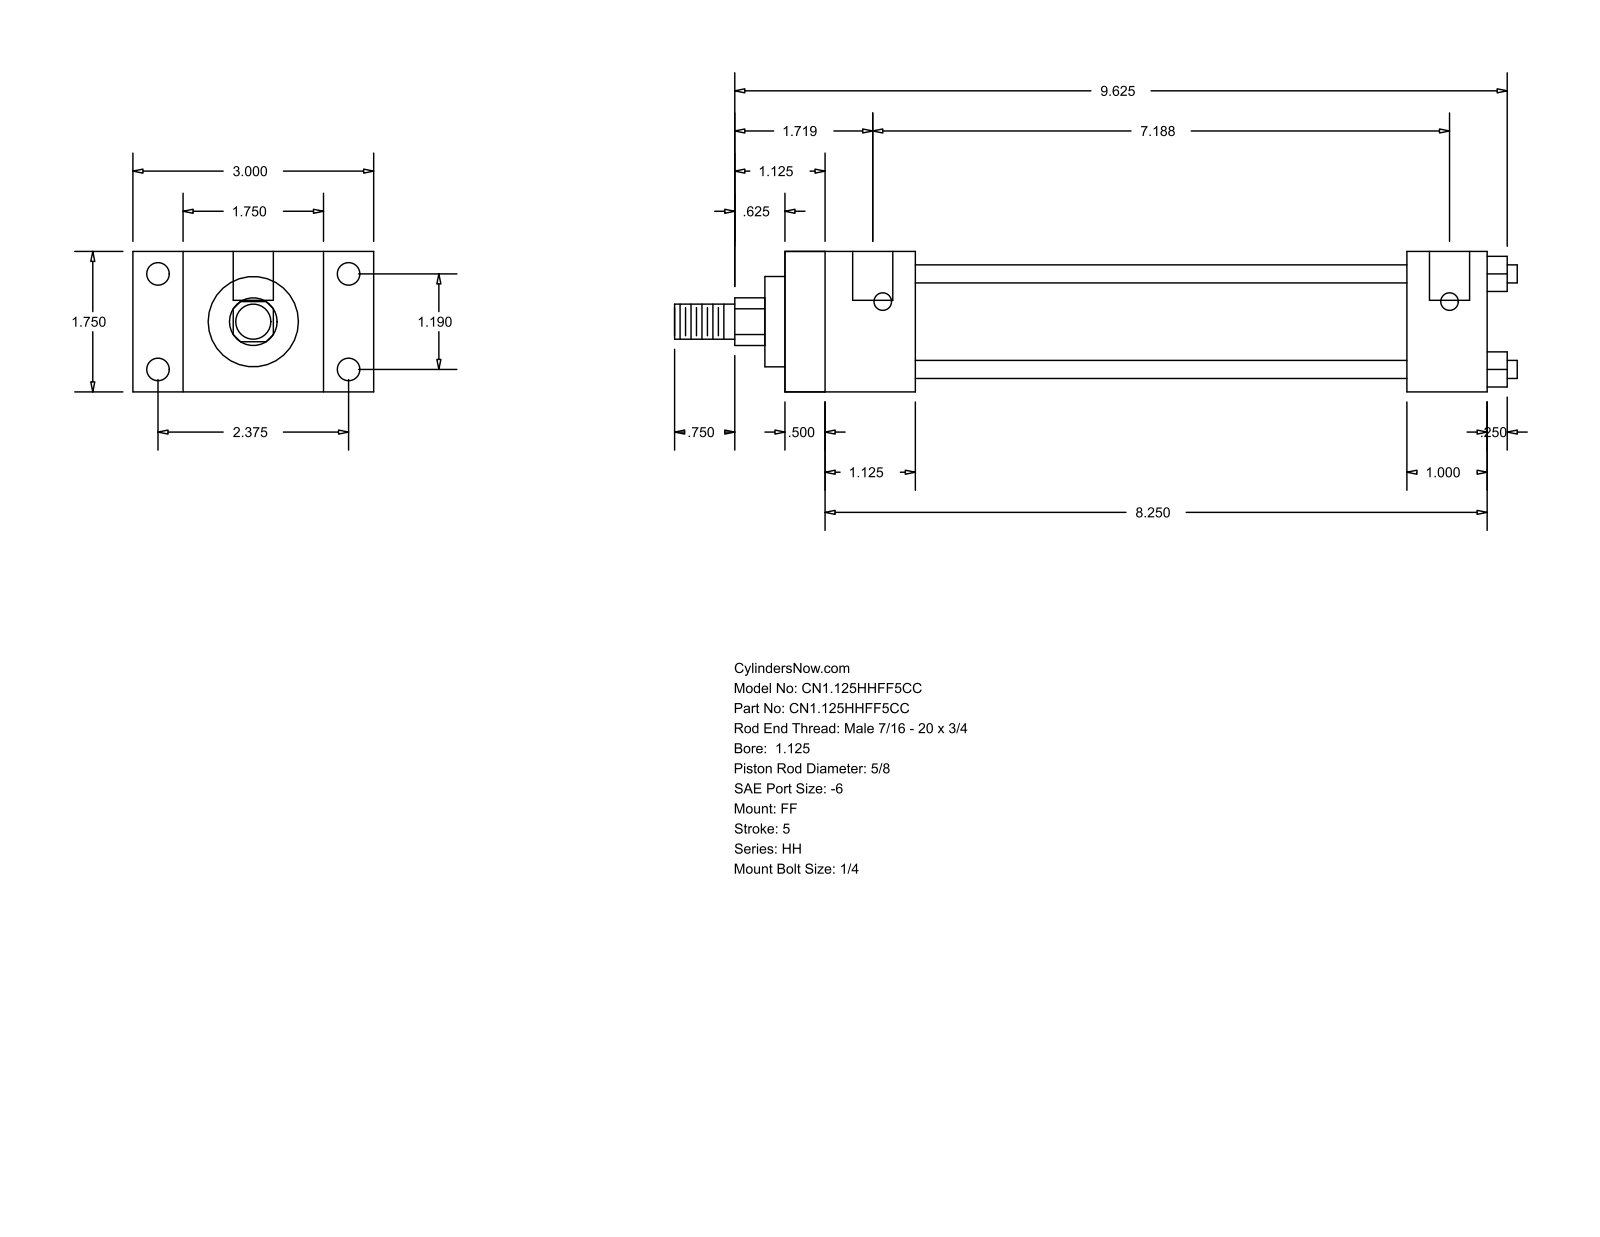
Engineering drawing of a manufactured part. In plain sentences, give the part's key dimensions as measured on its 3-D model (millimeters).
The part is named "HH_FF__0112_0.625". Its 3-D file was written by "GSSL Pune (CONFIG_CONTROL_DESIGN)". It is 0 solids with 92 faces: 64 planar, 28 cylindrical and 0 other. Overall it measures 266.7 by 76.2 by 44.45 millimeters. Round holes: 4 of diameter 5.56, 4 of diameter 7.14, 2 of diameter 12.7. Round bosses or shafts: 4 of diameter 5.71, 1 of diameter 34.92, 1 of diameter 28.57, 1 of diameter 15.88, 1 of diameter 11.11. Partial cylindrical surfaces (rounded edges, fillets, slot ends): 1 of radius 7.54. The main face-to-face distances are 44.46, 222.24, 12.69, 209.55, 15.87, 28.58, 60.33, 25.4, 41.27, 196.84. The hole center spacings are 30.22, 60.32, 67.47, 179.39, 3.17, 182.56.
